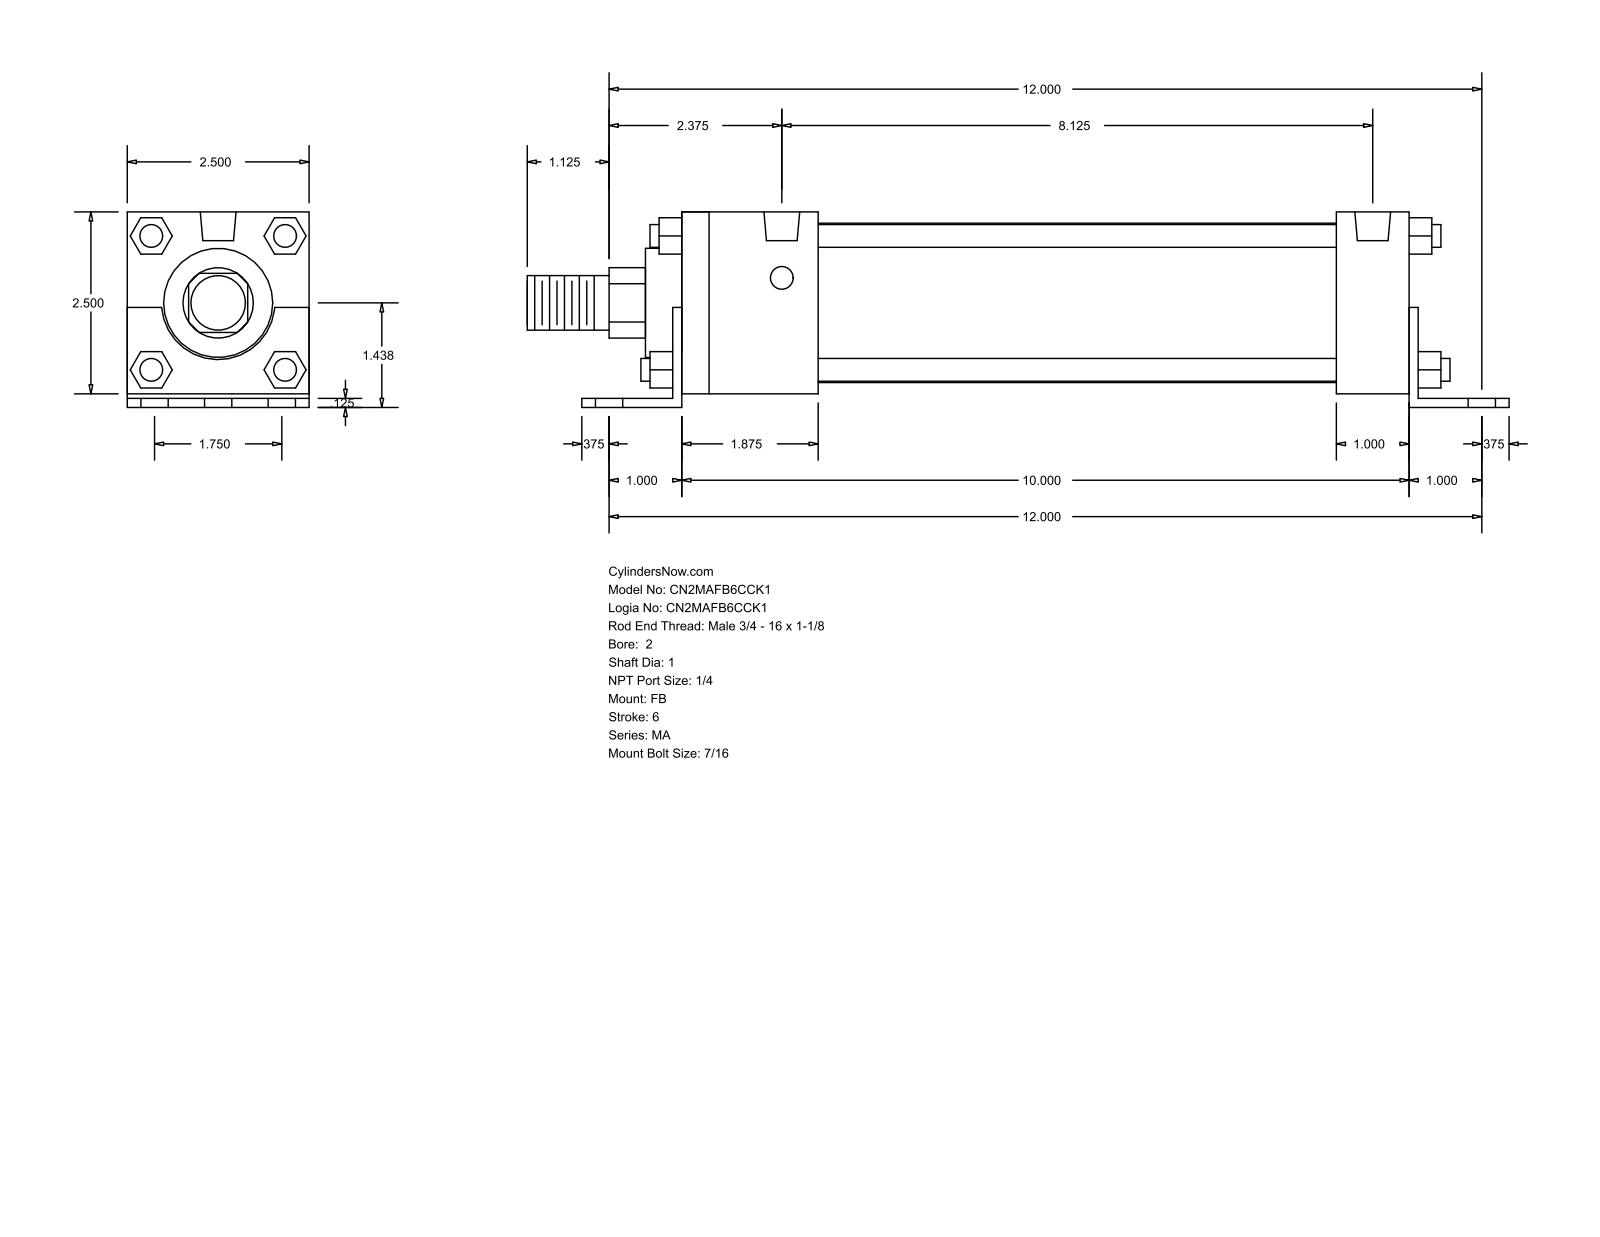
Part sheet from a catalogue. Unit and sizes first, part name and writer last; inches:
Units: inches
Overall size (bounding box): 13.5 × 2.687 × 2.5
Round holes (diameter × count): ⌀0.437 ×6, ⌀0.313 ×4, ⌀0.492 ×2
Round bosses / shafts (diameter × count): ⌀0.313 ×4, ⌀2.19 ×1, ⌀1.5 ×1, ⌀1 ×1, ⌀0.75 ×1
Partial cylindrical surfaces — rounded edges, fillets, slot ends (radius × count): R0.484 ×1, R0.78 ×1
Main face-to-face distances: 2.5, 0.125, 0.187, 2.687, 0.063, 2.563, 10.125, 0.5, 10, 1.125
Hole centre spacings: 0.875, 12.032, 12, 1.737, 1.75, 2.531, 8.125, 9.665
Bodies: 0 solids, 140 faces (105 planar, 35 cylindrical, 0 other)
Part name (STEP PRODUCT): MA_FB__0200_1
STEP written by: GSSL Pune (CONFIG_CONTROL_DESIGN)
